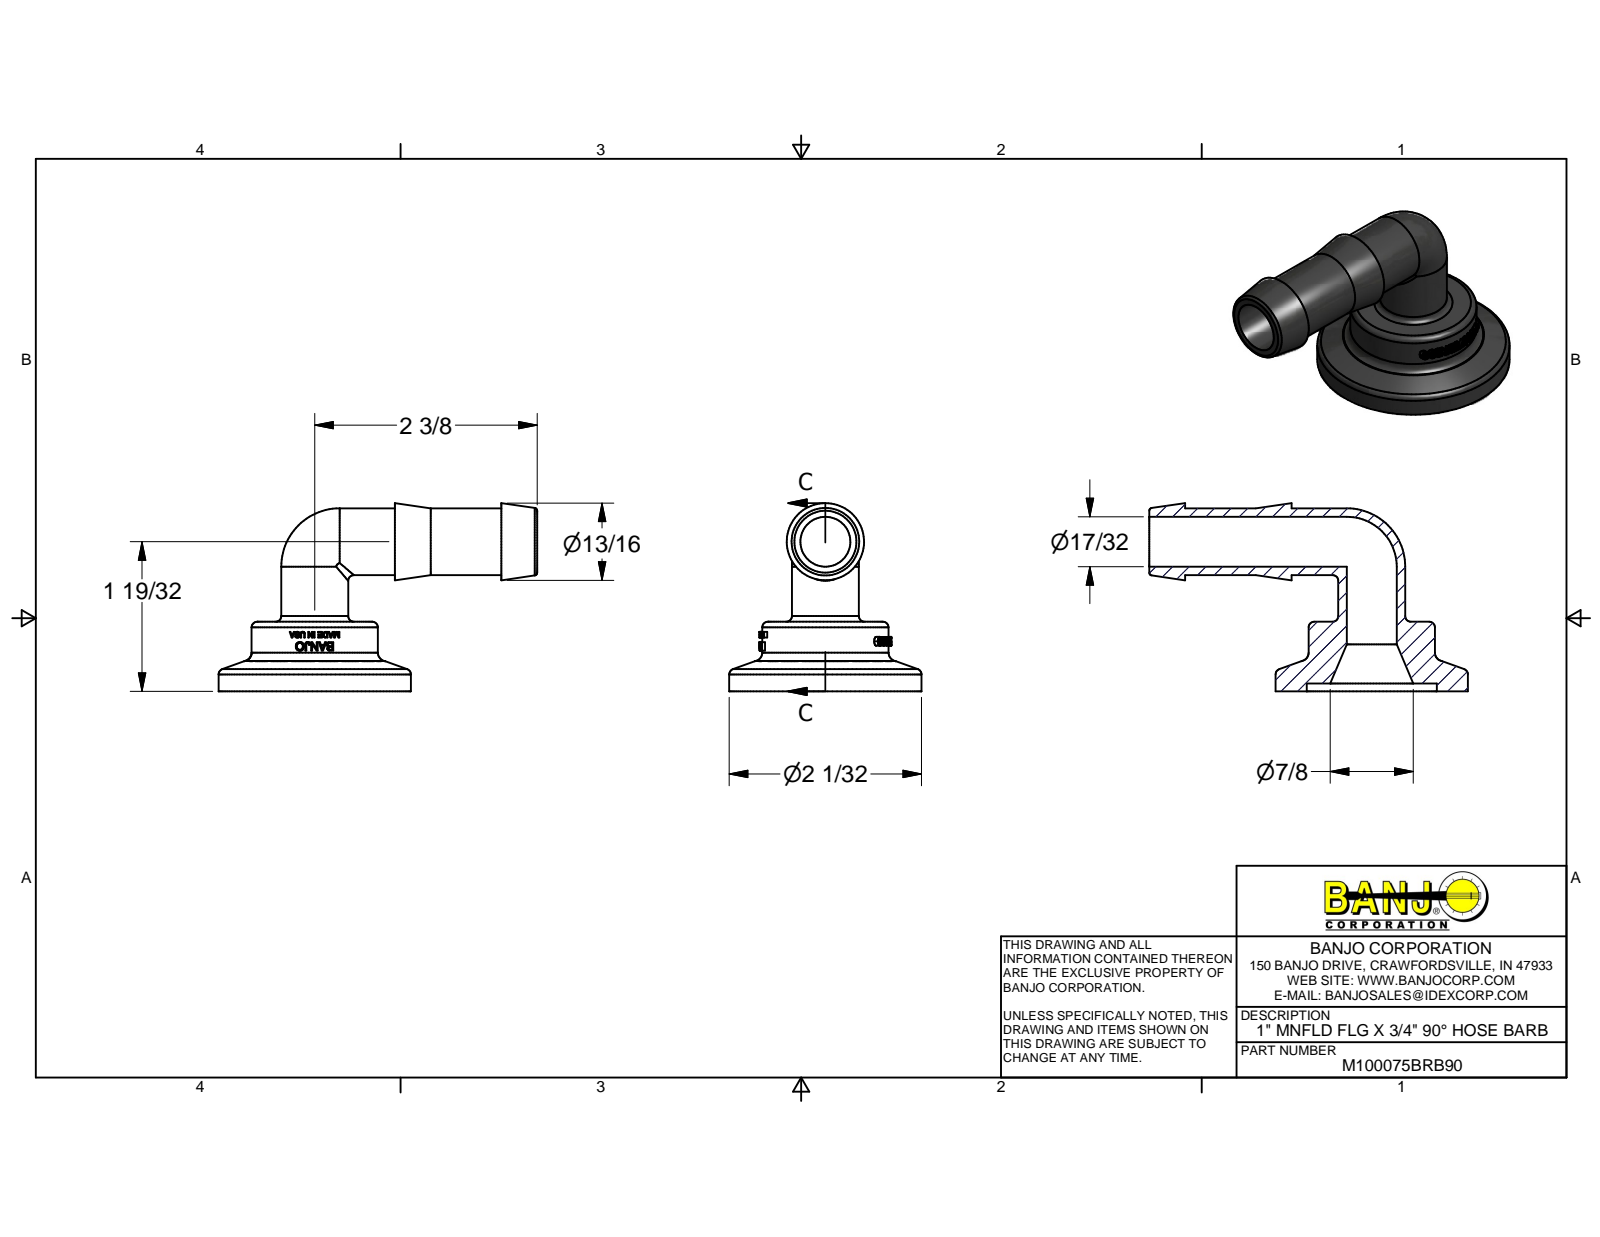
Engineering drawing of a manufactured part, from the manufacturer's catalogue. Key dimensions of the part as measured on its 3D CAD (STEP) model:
Part name (STEP PRODUCT): M100075BRB90
STEP written by: Autodesk Inventor 2014 (AUTOMOTIVE_DESIGN)
Units: millimetres
Bodies: 1 solid, 427 faces (189 planar, 51 cylindrical, 187 other)
Overall size (bounding box): 85.85 × 51.82 × 50.8
Volume: 29 725 mm³ · Surface area: 14 923 mm²
Round holes (diameter × count): ⌀13.46 ×2, ⌀35.05 ×1
Round bosses / shafts (diameter × count): ⌀18.03 ×2, ⌀51.82 ×1, ⌀34.04 ×1
Partial cylindrical surfaces — rounded edges, fillets, slot ends (radius × count): R17.78 ×1
Main face-to-face distances: 2.14, 18.8, 16.66, 28.7, 38.35, 9.65, 12.38, 1.38, 0.87, 10.24
